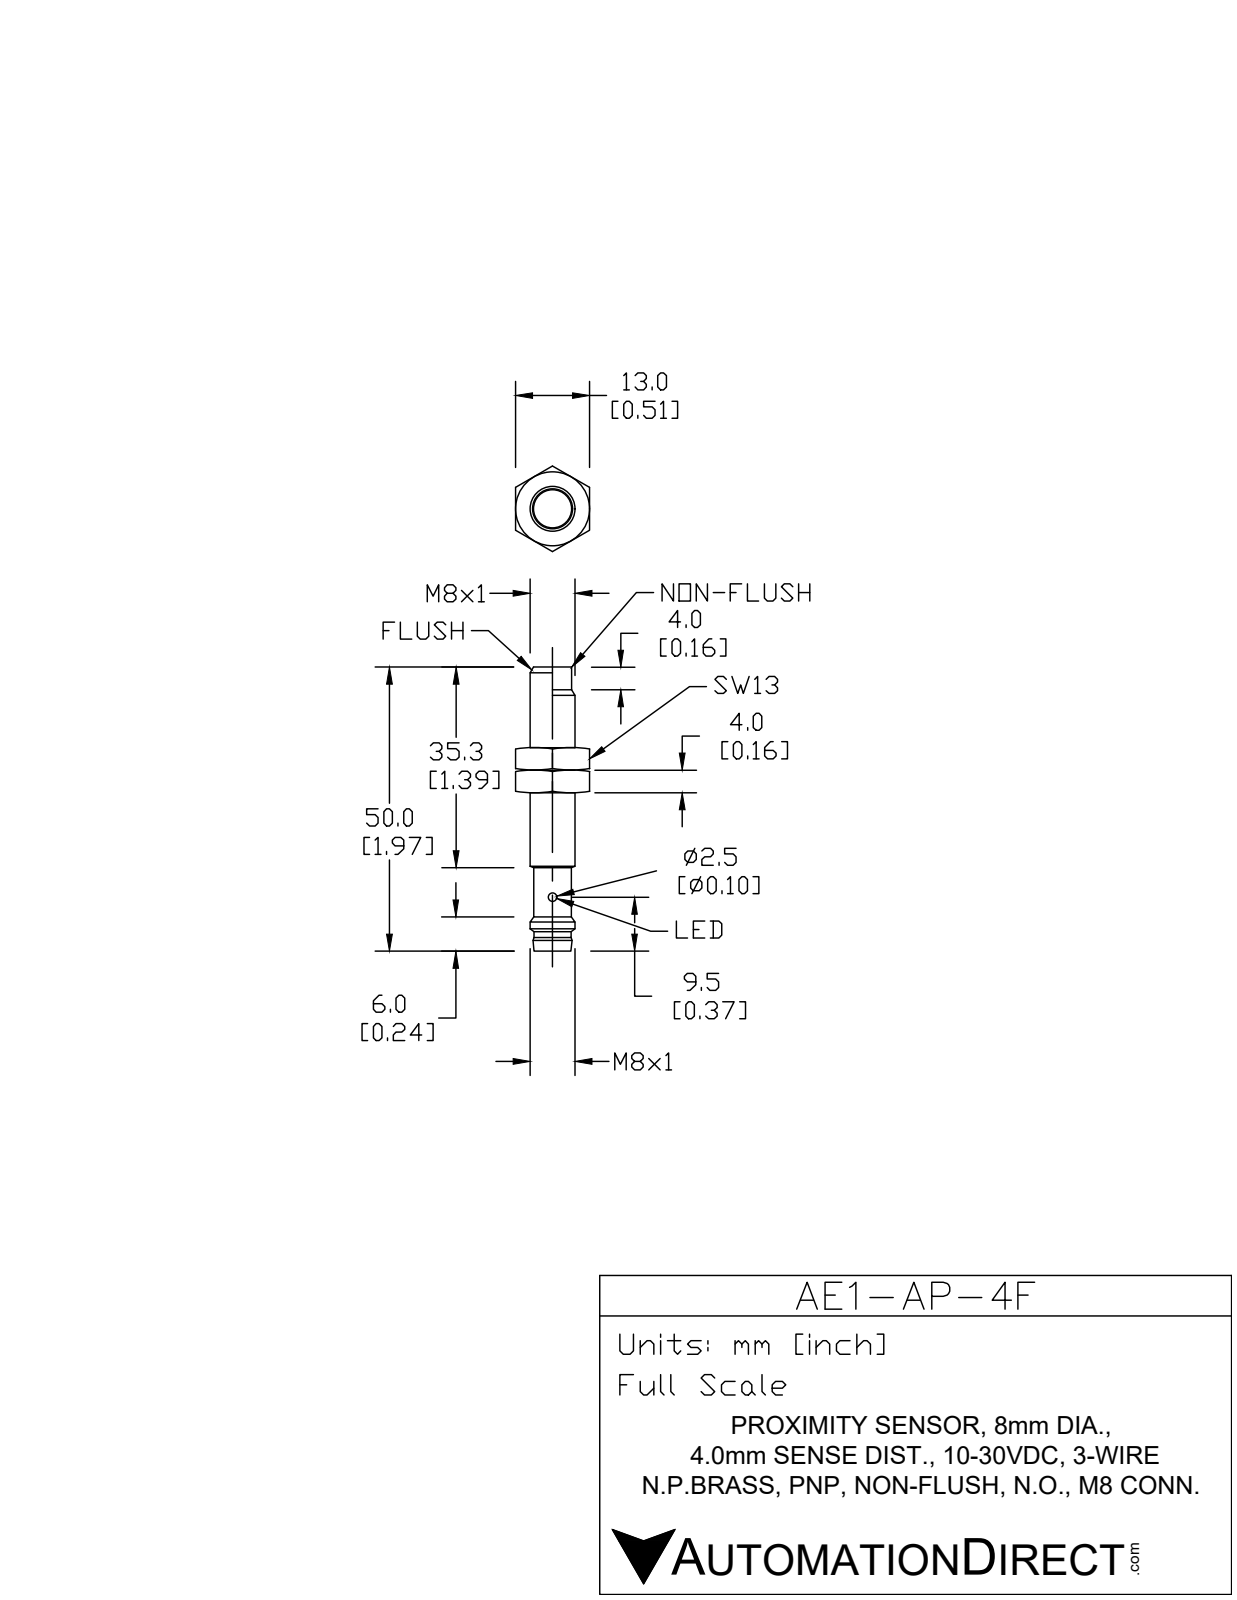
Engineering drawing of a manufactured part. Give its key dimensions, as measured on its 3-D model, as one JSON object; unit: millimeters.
{"part_name": "AE1-AP-4A", "step_written_by": "SolidWorks 2017 (AUTOMOTIVE_DESIGN)", "units": "millimeters", "bodies": {"solids": 4, "faces": 30, "planar": 10, "cylindrical": 12, "other": 8}, "overall_size": [82.6, 8, 8], "volume_mm3": 2380, "surface_area_mm2": 1726, "round_holes": [[3.1, 1], [5.8, 1]], "round_bosses_or_shafts": [[8, 1], [6.5, 1], [6.5, 1]], "face_to_face_distances": [36.2, 4, 40.2, 44.5, 40.5, 4.3, 2.4, 42.6, 38.6, 1.9], "hole_center_spacings": [1.1]}
